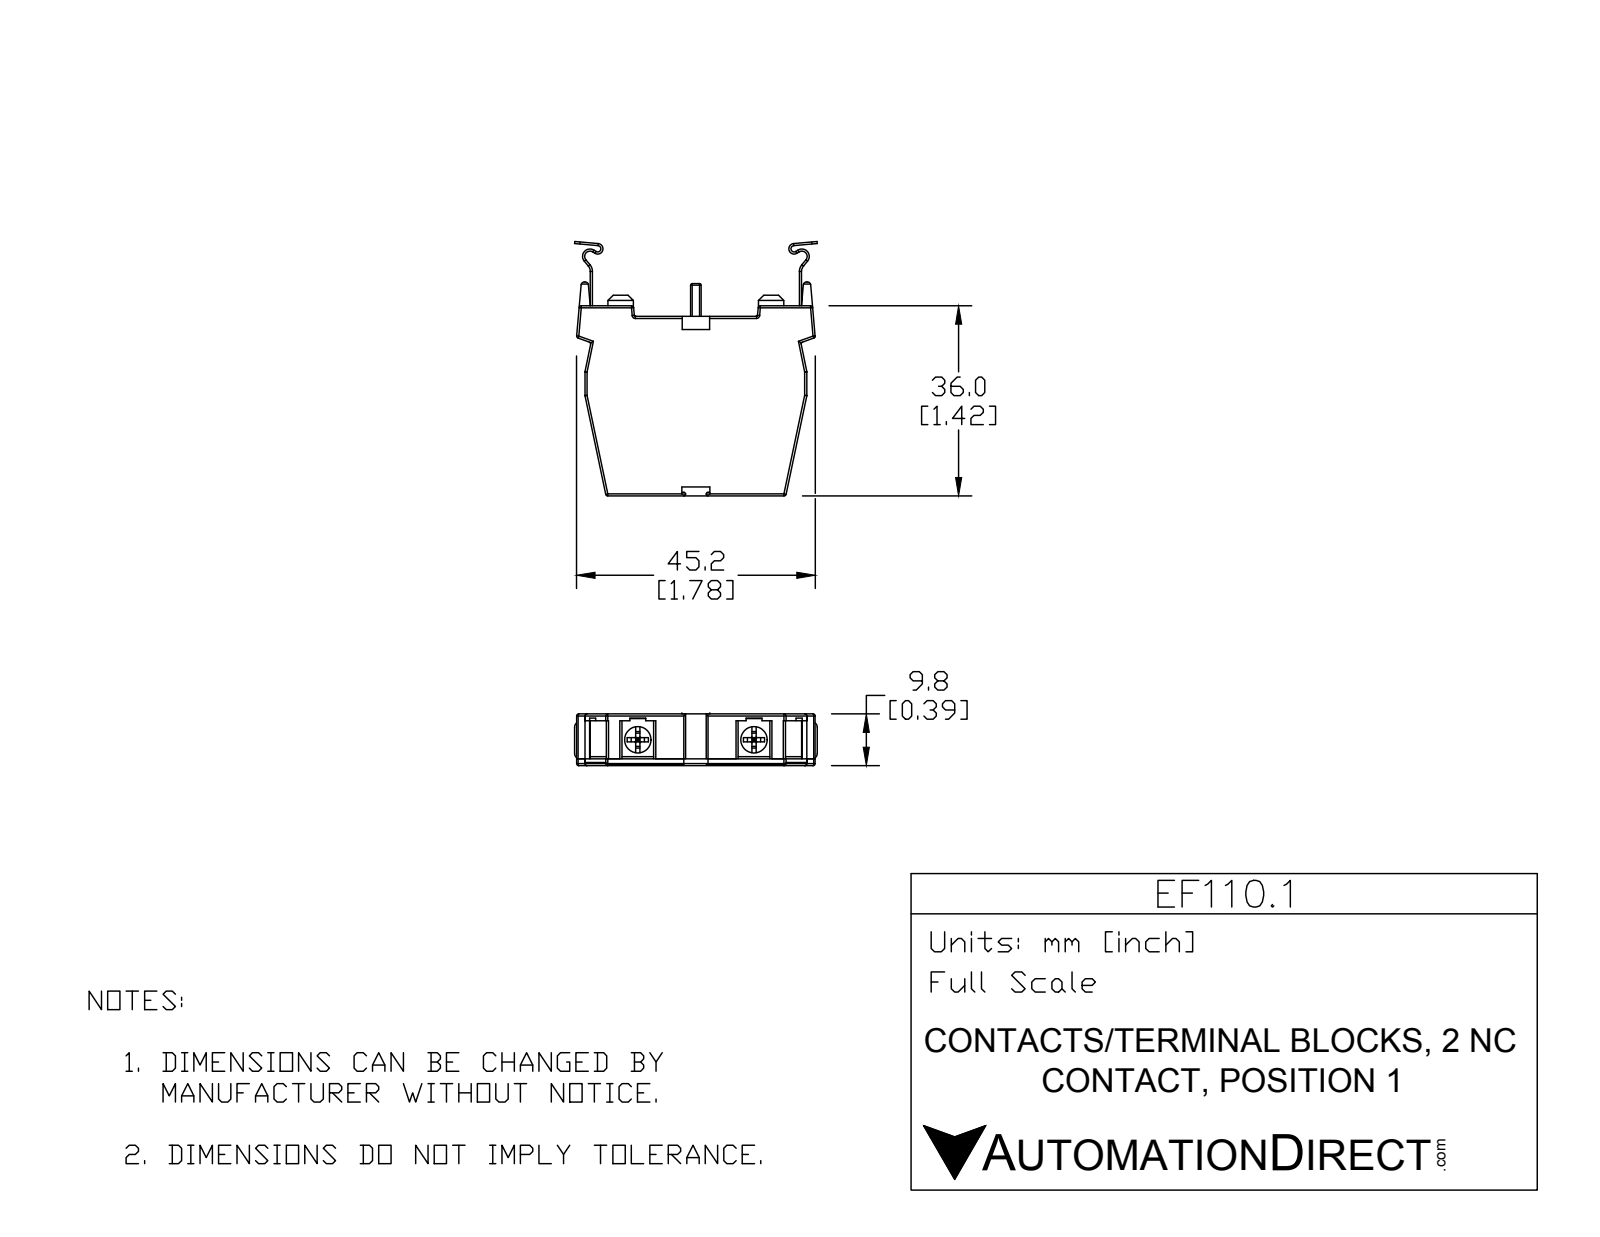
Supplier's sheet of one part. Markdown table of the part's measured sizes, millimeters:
| quantity | value |
| --- | --- |
| part name | EF110.1 |
| STEP written by | SolidWorks 2015 (AUTOMOTIVE_DESIGN) |
| units | millimeters |
| bodies | 7 solids, 299 faces (173 planar, 104 cylindrical, 22 other) |
| overall size | 48.16 × 46.28 × 9.8 |
| volume | 12 135 mm³ |
| surface area | 6 604 mm² |
| round holes (diameter × count) | 5 × 4 |
| round bosses / shafts (diameter × count) | 4 × 4, 4.75 × 2 |
| partial cylindrical surfaces (radius × count) | 0.25 × 44, 0.5 × 8, 1 × 6, 0.6 × 4, 0.6 × 2, 1 × 2, 1.4 × 2, 1.6 × 2 |
| main face-to-face distances | 9.8, 1.4, 8.4, 34, 7, 2, 0.4, 3.18, 37.18, 36 |
| hole center spacings | 21.81 |
